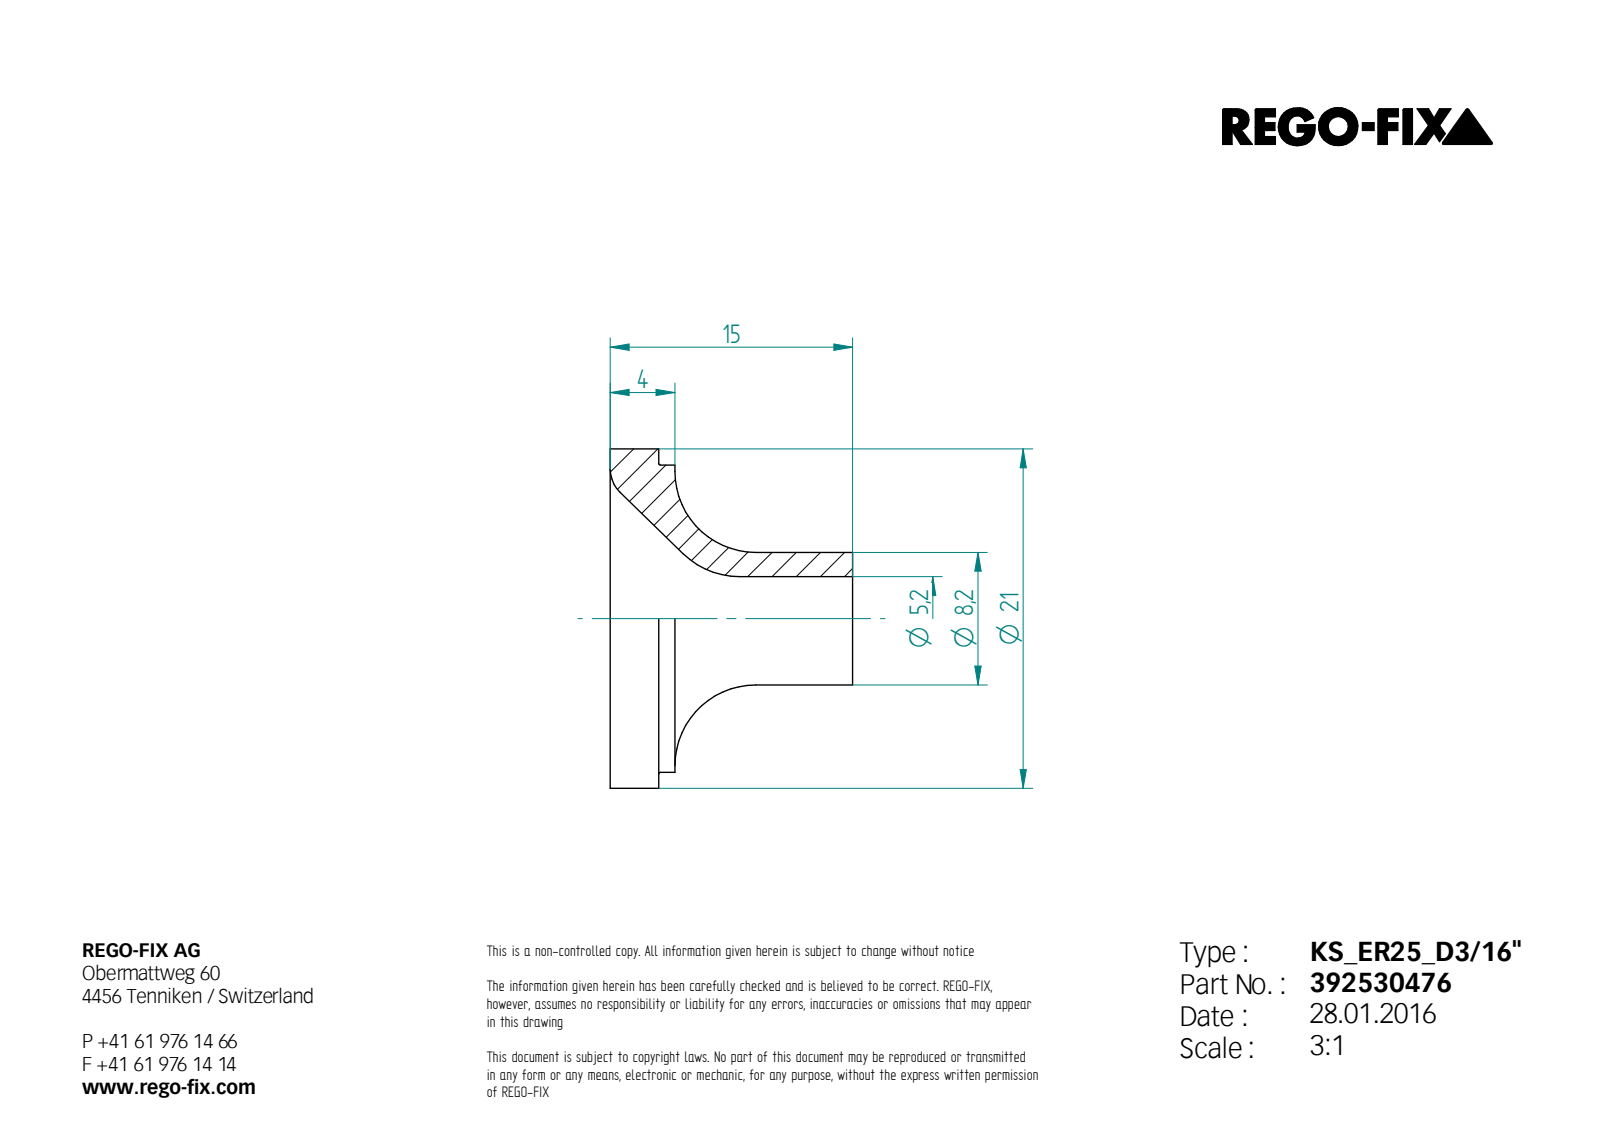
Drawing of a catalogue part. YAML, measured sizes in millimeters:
step_written_by: "Unknown (AUTOMOTIVE_DESIGN)"
units: millimeters
bodies: {solids: 1, faces: 13, planar: 4, cylindrical: 4, other: 5}
overall_size: [21, 21, 15]
volume: 1253
surface_area: 1374
round_holes:
  - {diameter: 5.2, count: 1}
round_bosses_or_shafts:
  - {diameter: 21, count: 1}
  - {diameter: 19, count: 1}
  - {diameter: 8.2, count: 1}
face_to_face_distances: [3, 15, 12, 4, 1, 11]
